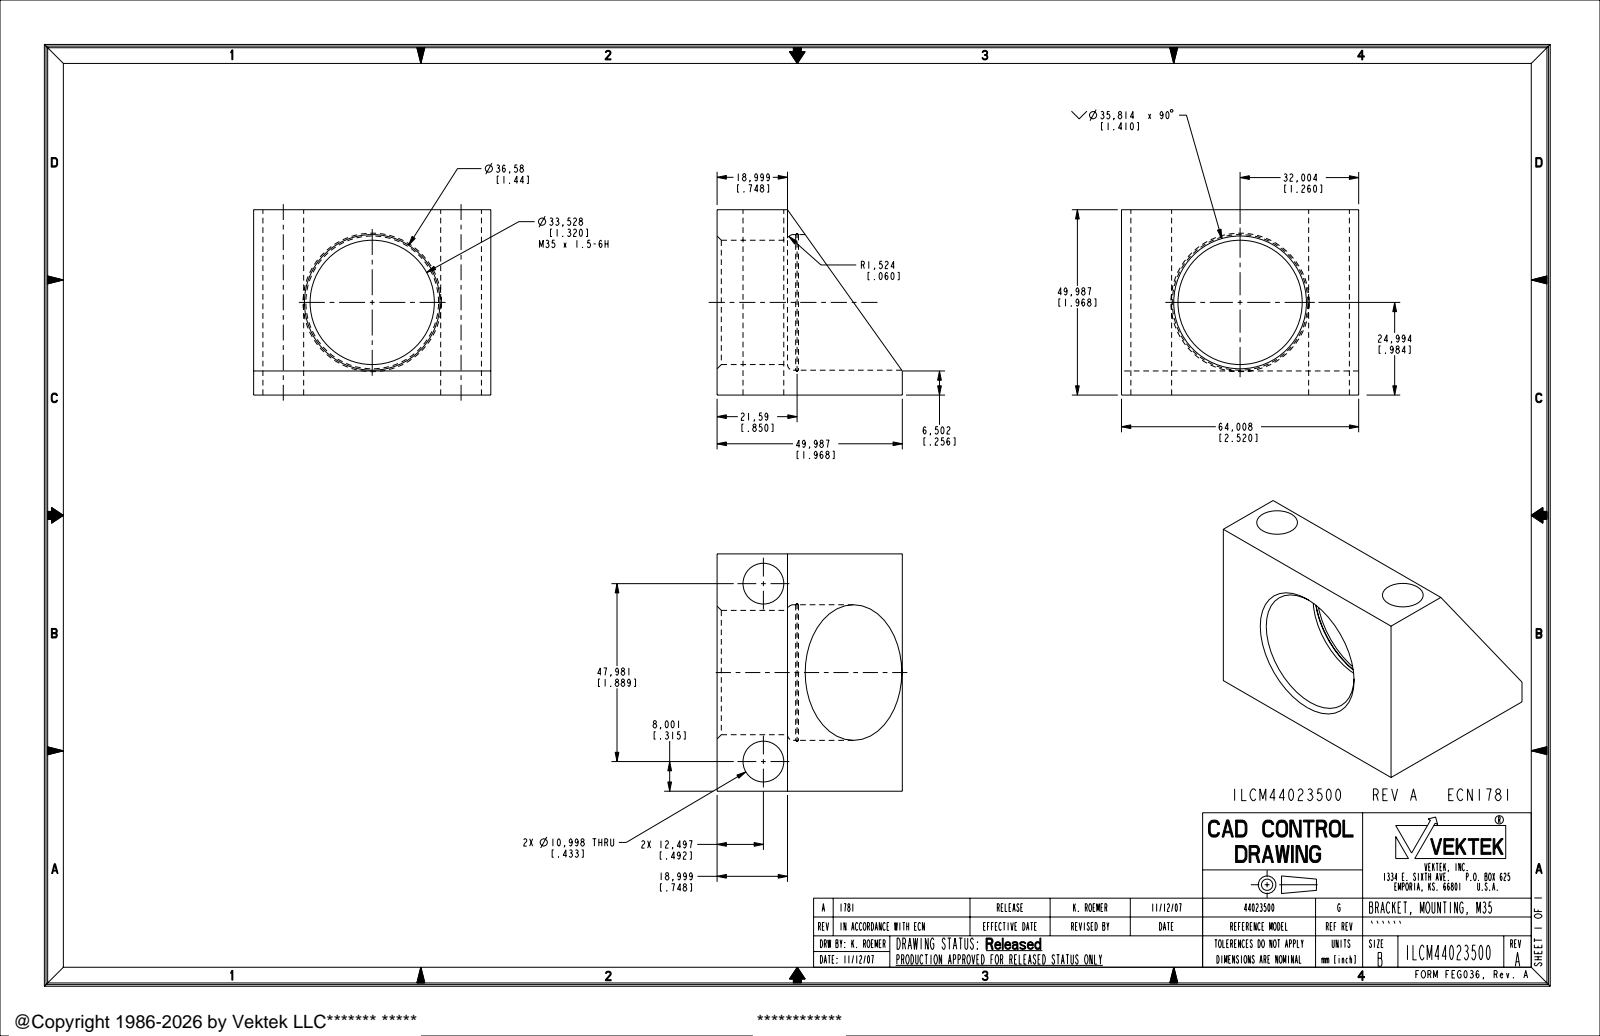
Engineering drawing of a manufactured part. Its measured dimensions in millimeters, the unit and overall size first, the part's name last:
Units: millimetres
Overall size (bounding box): 64.01 × 49.99 × 49.99
Round holes (diameter × count): ⌀11 ×2, ⌀33.53 ×1, ⌀36.58 ×1
Main face-to-face distances: 64.01, 49.99
Hole centre spacings: 47.98
Volume: 71 796 mm³ · Surface area: 20 109 mm²
Bodies: 1 solid, 25 faces (7 planar, 10 cylindrical, 8 other)
Part name (STEP PRODUCT): ILCM44023500
STEP written by: PRO/ENGINEER BY PARAMETRIC TECHNOLOGY CORPORATION, 2005180 (AUTOMOTIVE_DESIGN_CC2)
